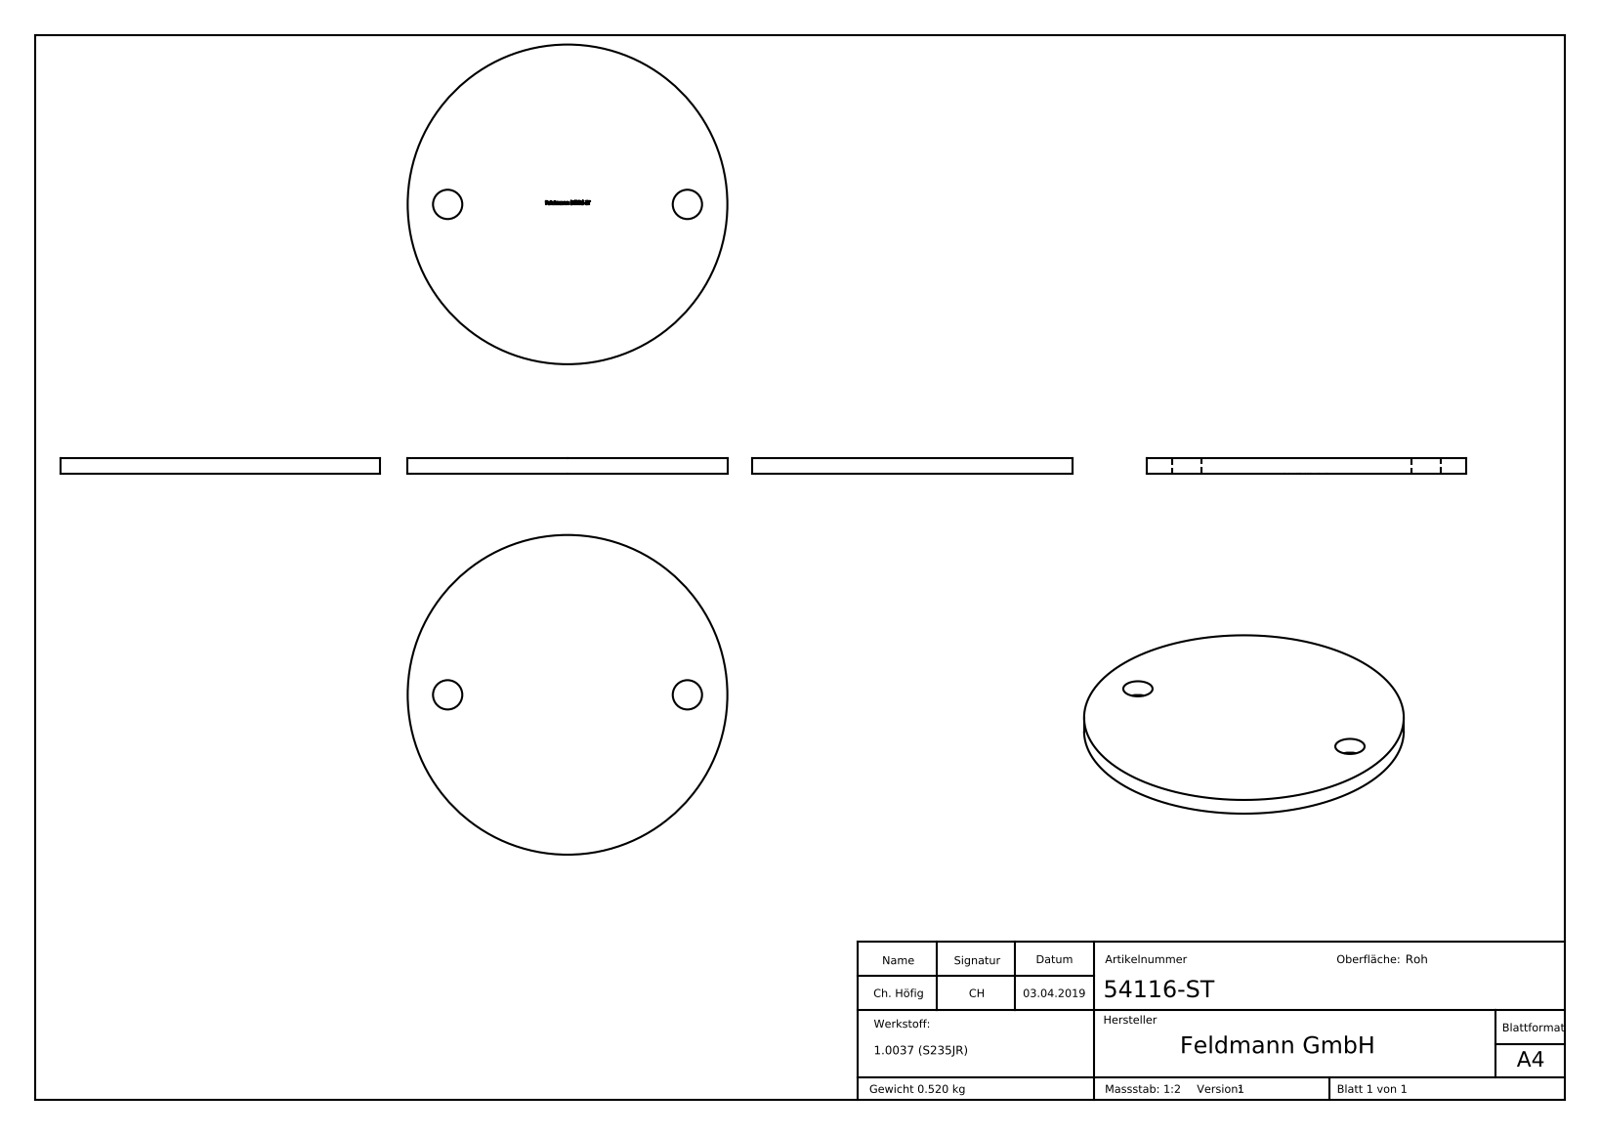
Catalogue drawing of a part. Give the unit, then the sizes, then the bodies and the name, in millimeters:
Units: millimetres
Overall size (bounding box): 120 × 120 × 6
Round holes (diameter × count): ⌀11 ×2
Round bosses / shafts (diameter × count): ⌀120 ×1
Main face-to-face distances: 6, 5.9, 1.02, 9.72, 10.74, 2.02, 1.32, 11.74, 12.76, 4.43
Hole centre spacings: 90
Volume: 66 718 mm³ · Surface area: 24 924 mm²
Bodies: 1 solid, 211 faces (125 planar, 6 cylindrical, 80 other)
Part name (STEP PRODUCT): 54116-ST
STEP written by: SolidWorks 2015 (CONFIG_CONTROL_DESIGN)
